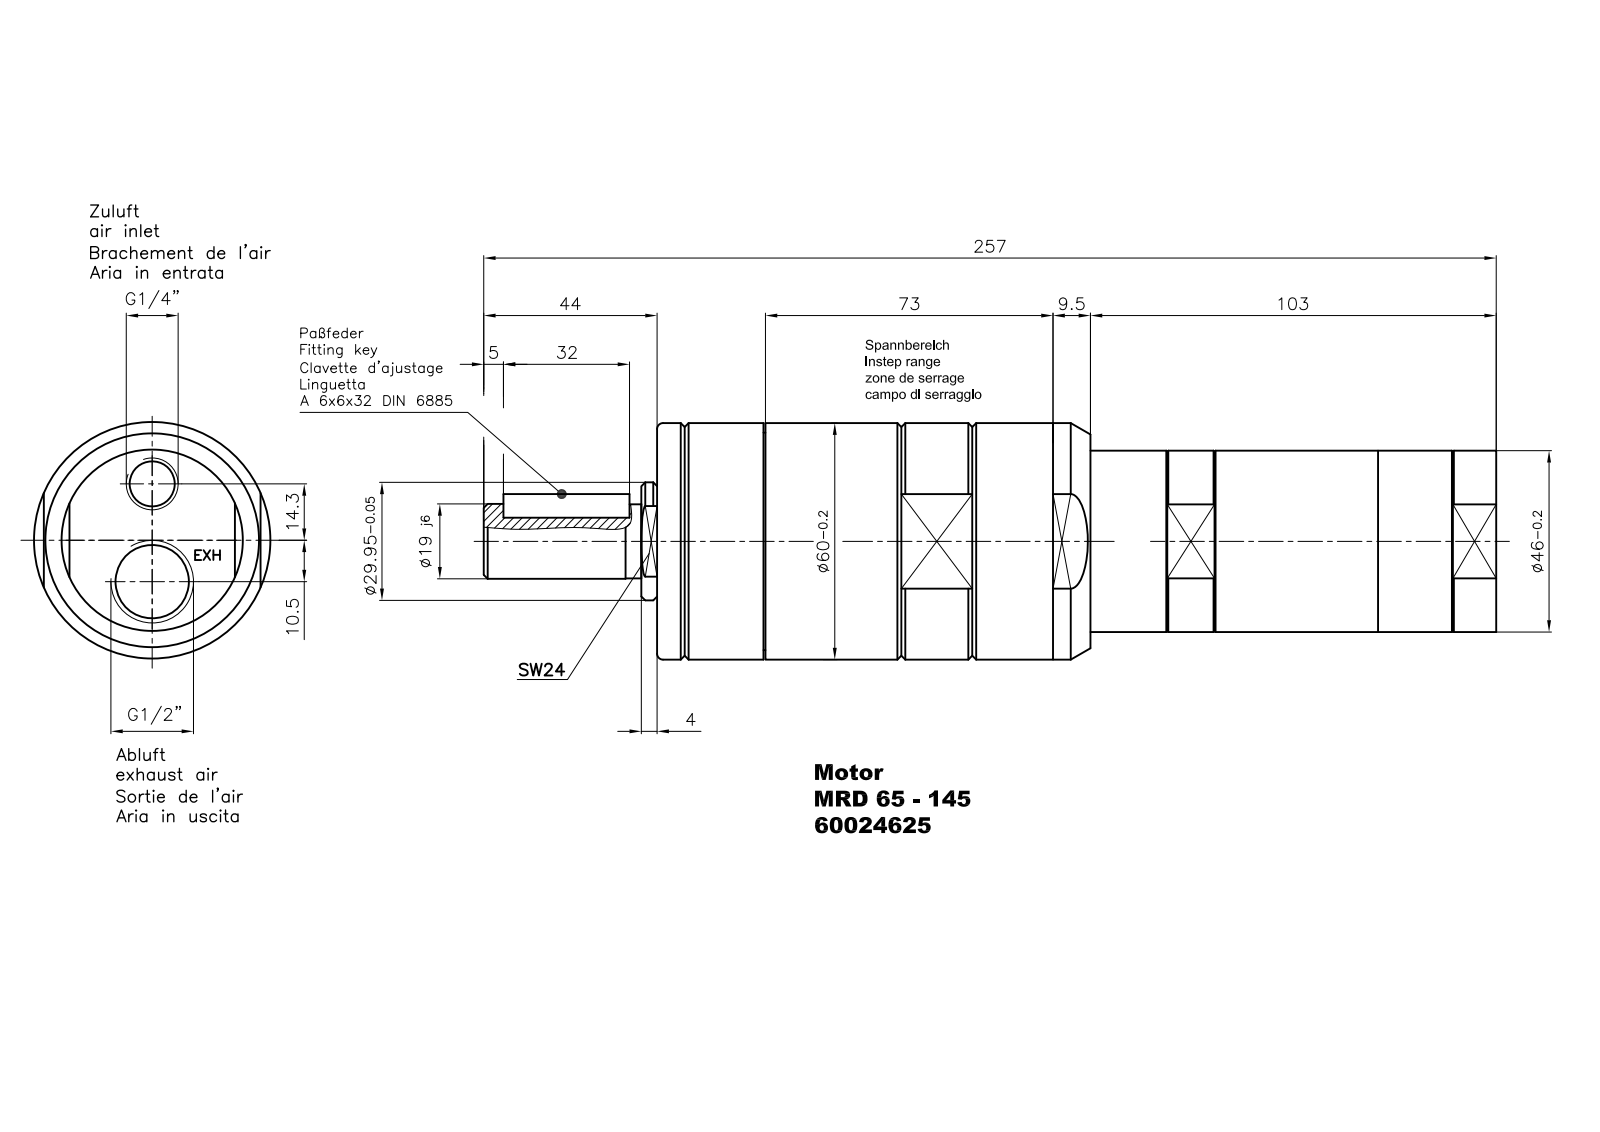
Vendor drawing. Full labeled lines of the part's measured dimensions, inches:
Part name (STEP PRODUCT): MRD 65-257
STEP written by: Autodesk Inventor 2012 (AUTOMOTIVE_DESIGN)
Units: inches
Bodies: 1 solid, 149 faces (83 planar, 34 cylindrical, 32 other)
Overall size (bounding box): 10.118 × 2.362 × 2.362
Volume: 29.58 in³ · Surface area: 78.98 in²
Round holes (diameter × count): ⌀0.061 ×1, ⌀0.063 ×1, ⌀0.217 ×1, ⌀0.451 ×1, ⌀0.733 ×1, ⌀0.787 ×1, ⌀1.378 ×1, ⌀1.831 ×1
Round bosses / shafts (diameter × count): ⌀2.362 ×1, ⌀2.172 ×1, ⌀1.811 ×1, ⌀1.179 ×1, ⌀0.748 ×1, ⌀0.74 ×1, ⌀0.197 ×1
Partial cylindrical surfaces — rounded edges, fillets, slot ends (radius × count): R0.118 ×2
Main face-to-face distances: 3.957, 8.386, 4.429, 2.874, 3.248, 0.256, 4.055, 2.165, 4.331, 0.374
Hole centre spacings: 0.413, 0.563, 0.976
